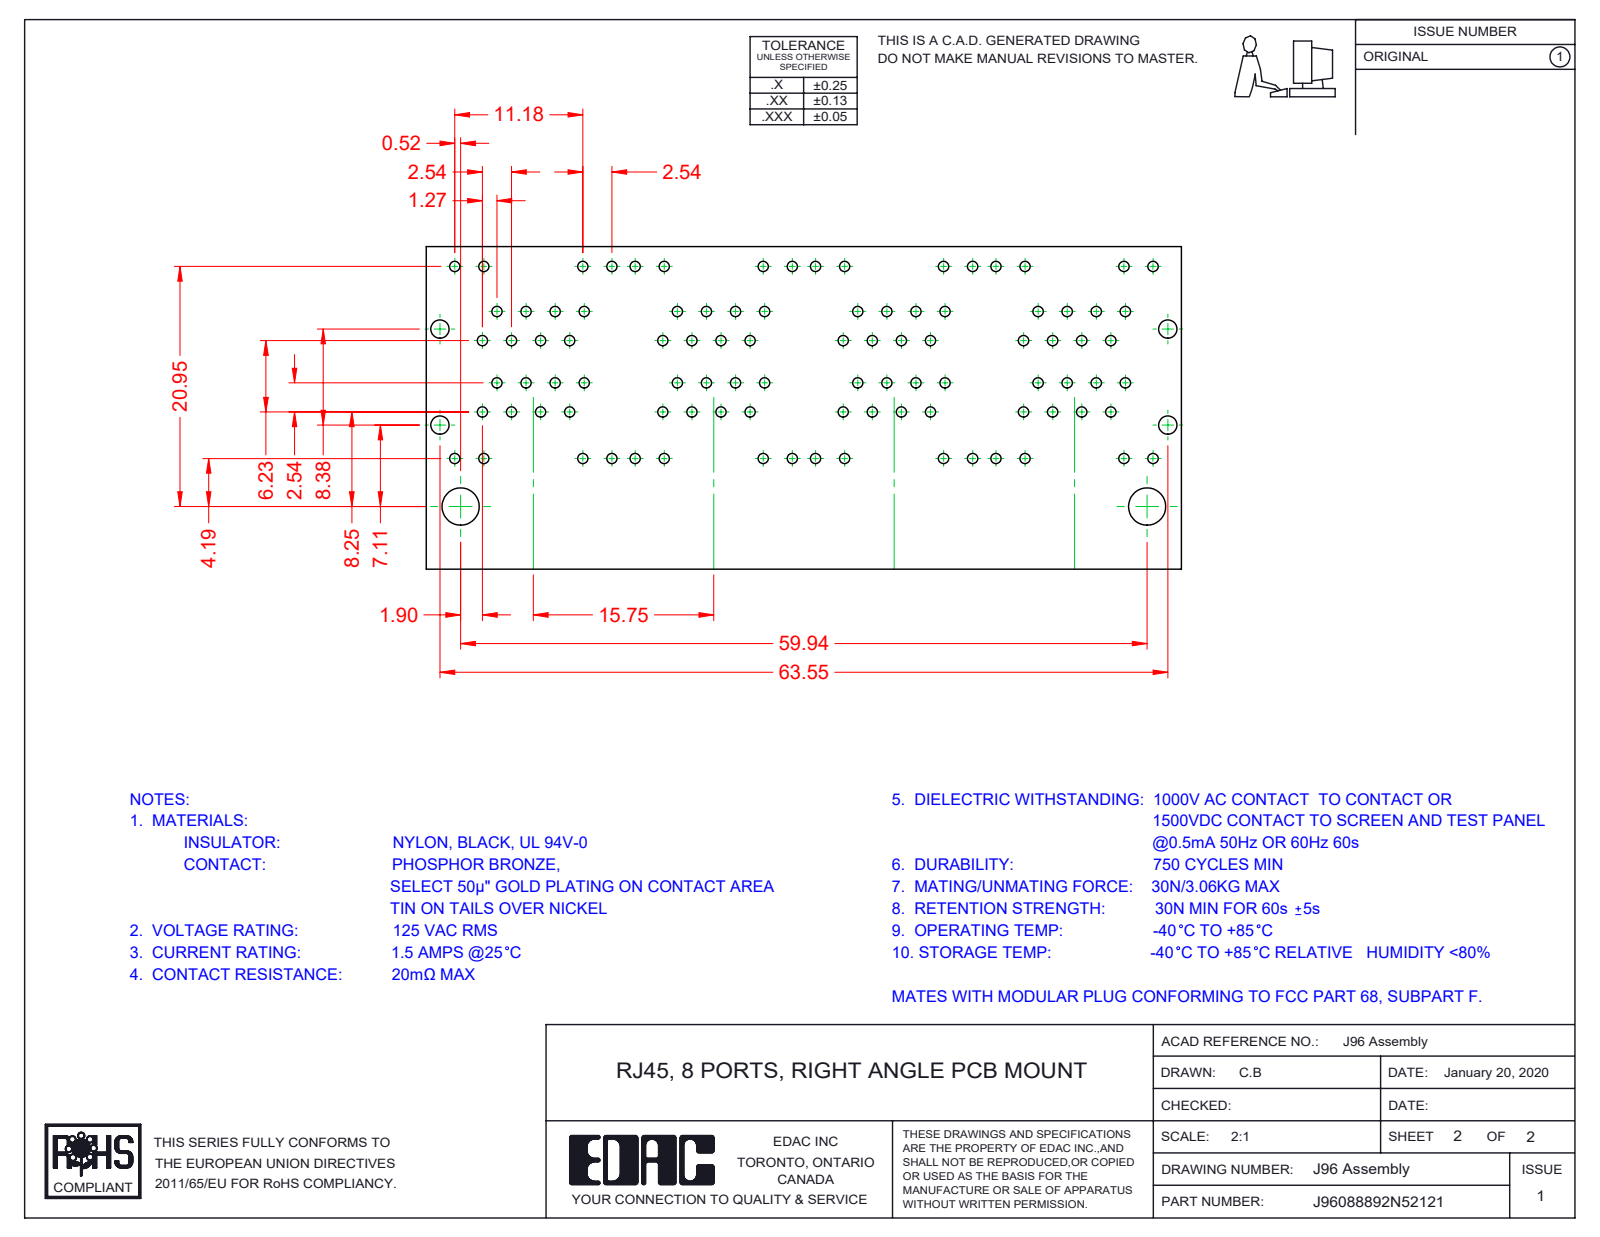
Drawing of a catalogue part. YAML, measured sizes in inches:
part_name: "J96088892N52121; 96 Contacts Lower; 96 Insulator_8 Ports; 96 Contact Lock Lower (+8 more)"
step_written_by: "SolidWorks 2016 (CONFIG_CONTROL_DESIGN)"
units: inches
bodies: {solids: 96, faces: 7658, planar: 6069, cylindrical: 1323, other: 266}
overall_size: [2.522, 1.165, 1.129]
volume: 1.474
surface_area: 98.67
round_holes:
  - {diameter: 0.067, count: 3}
round_bosses_or_shafts:
  - {diameter: 0.066, count: 3}
partial_cylinders:
  - {radius: 0.01, count: 124}
  - {radius: 0.014, count: 73}
  - {radius: 0.039, count: 72}
  - {radius: 0.02, count: 49}
  - {radius: 0.036, count: 32}
  - {radius: 0.008, count: 21}
  - {radius: 0.028, count: 11}
  - {radius: 0.009, count: 8}
face_to_face_distances: [0.62, 0.014, 0.392, 0.046, 0.063, 0.021, 0.393, 0.401, 0.499, 0.133]
hole_center_spacings: [0.62, 1.24]
